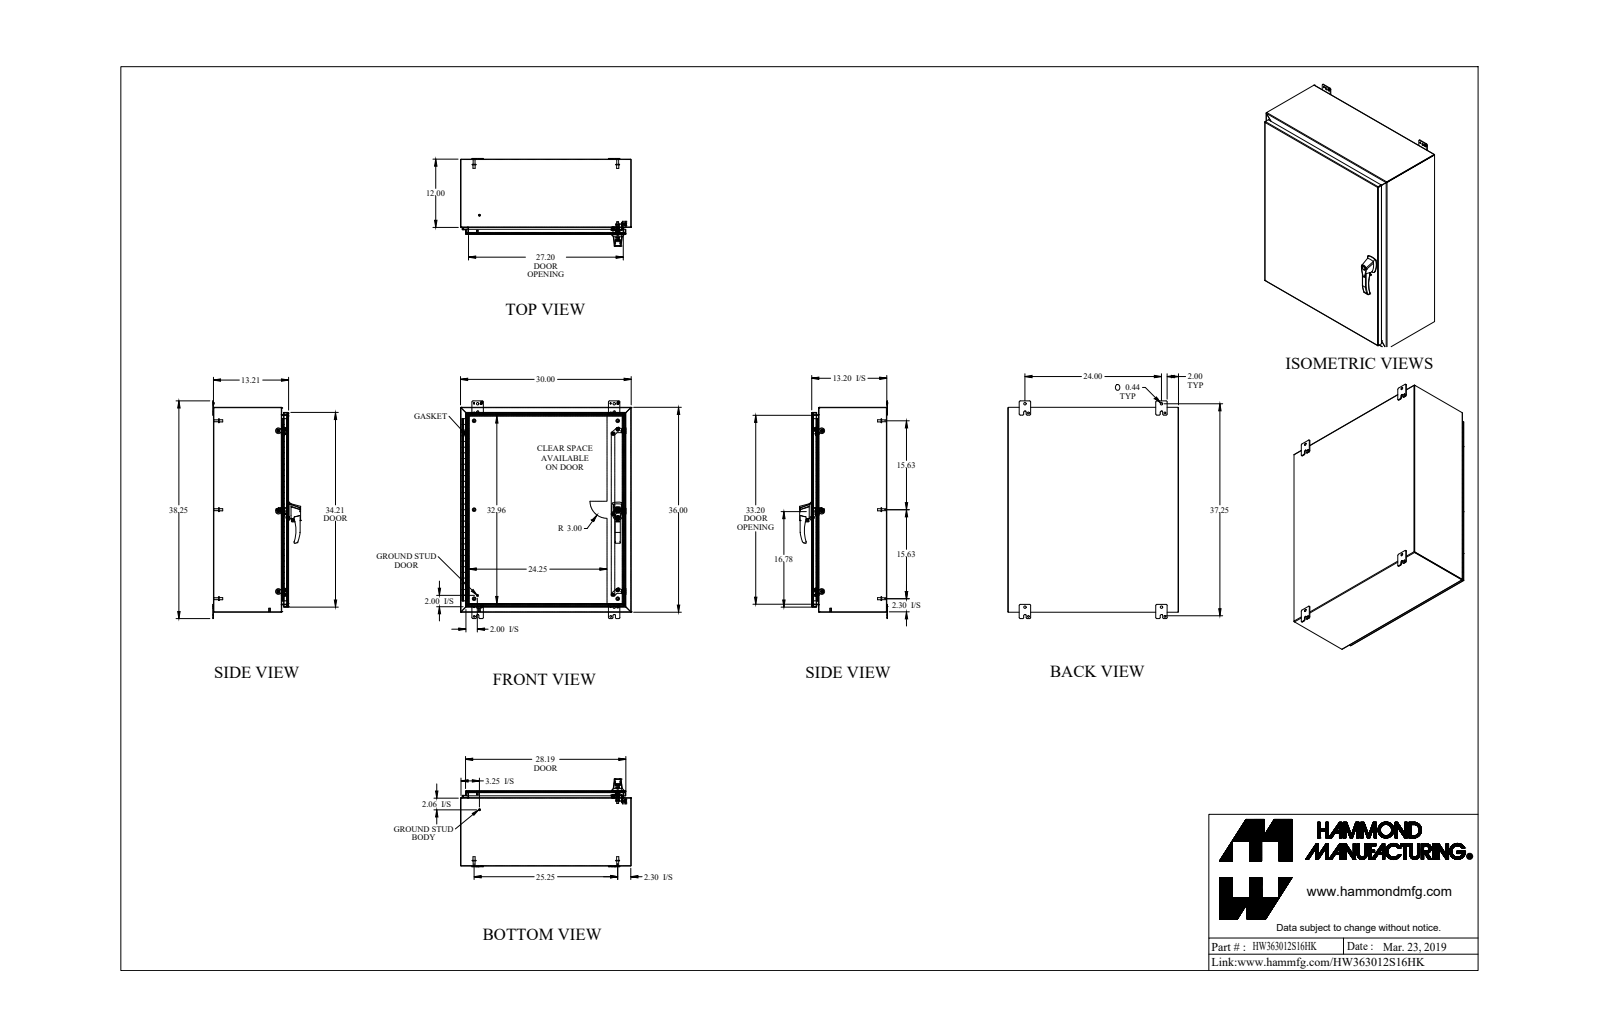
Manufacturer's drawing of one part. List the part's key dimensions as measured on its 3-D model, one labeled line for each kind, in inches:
Part name (STEP PRODUCT): HW363012S16HK
STEP written by: SolidWorks 2018 (AUTOMOTIVE_DESIGN)
Units: inches
Bodies: 46 solids, 1506 faces (704 planar, 646 cylindrical, 156 other)
Overall size (bounding box): 38.25 × 30 × 15.45
Volume: 330.8 in³ · Surface area: 8 772 in²
Round holes (diameter × count): ⌀0.176 ×6, ⌀0.313 ×5, ⌀0.25 ×3, ⌀0.265 ×3, ⌀0.413 ×3, ⌀0.196 ×2, ⌀0.256 ×2, ⌀0.394 ×2, ⌀0.437 ×2, ⌀0.11 ×1, ⌀0.233 ×1, ⌀0.33 ×1
Round bosses / shafts (diameter × count): ⌀0.375 ×11, ⌀0.25 ×7, ⌀0.65 ×6, ⌀0.332 ×6, ⌀0.156 ×6, ⌀1 ×3, ⌀0.51 ×3, ⌀0.63 ×2
Partial cylindrical surfaces — rounded edges, fillets, slot ends (radius × count): R0.25 ×27, R0.188 ×24, R0.036 ×18, R0.108 ×18, R0.06 ×12, R0.125 ×9, R0.045 ×8, R0.218 ×8
Main face-to-face distances: 0.072, 0.072, 13.066, 13.138, 13.138, 13.21, 29.928, 35.928, 29.856, 30
Hole centre spacings: 1.111, 14.118, 14.119, 28.237, 14.119, 24, 24.724, 37.38
